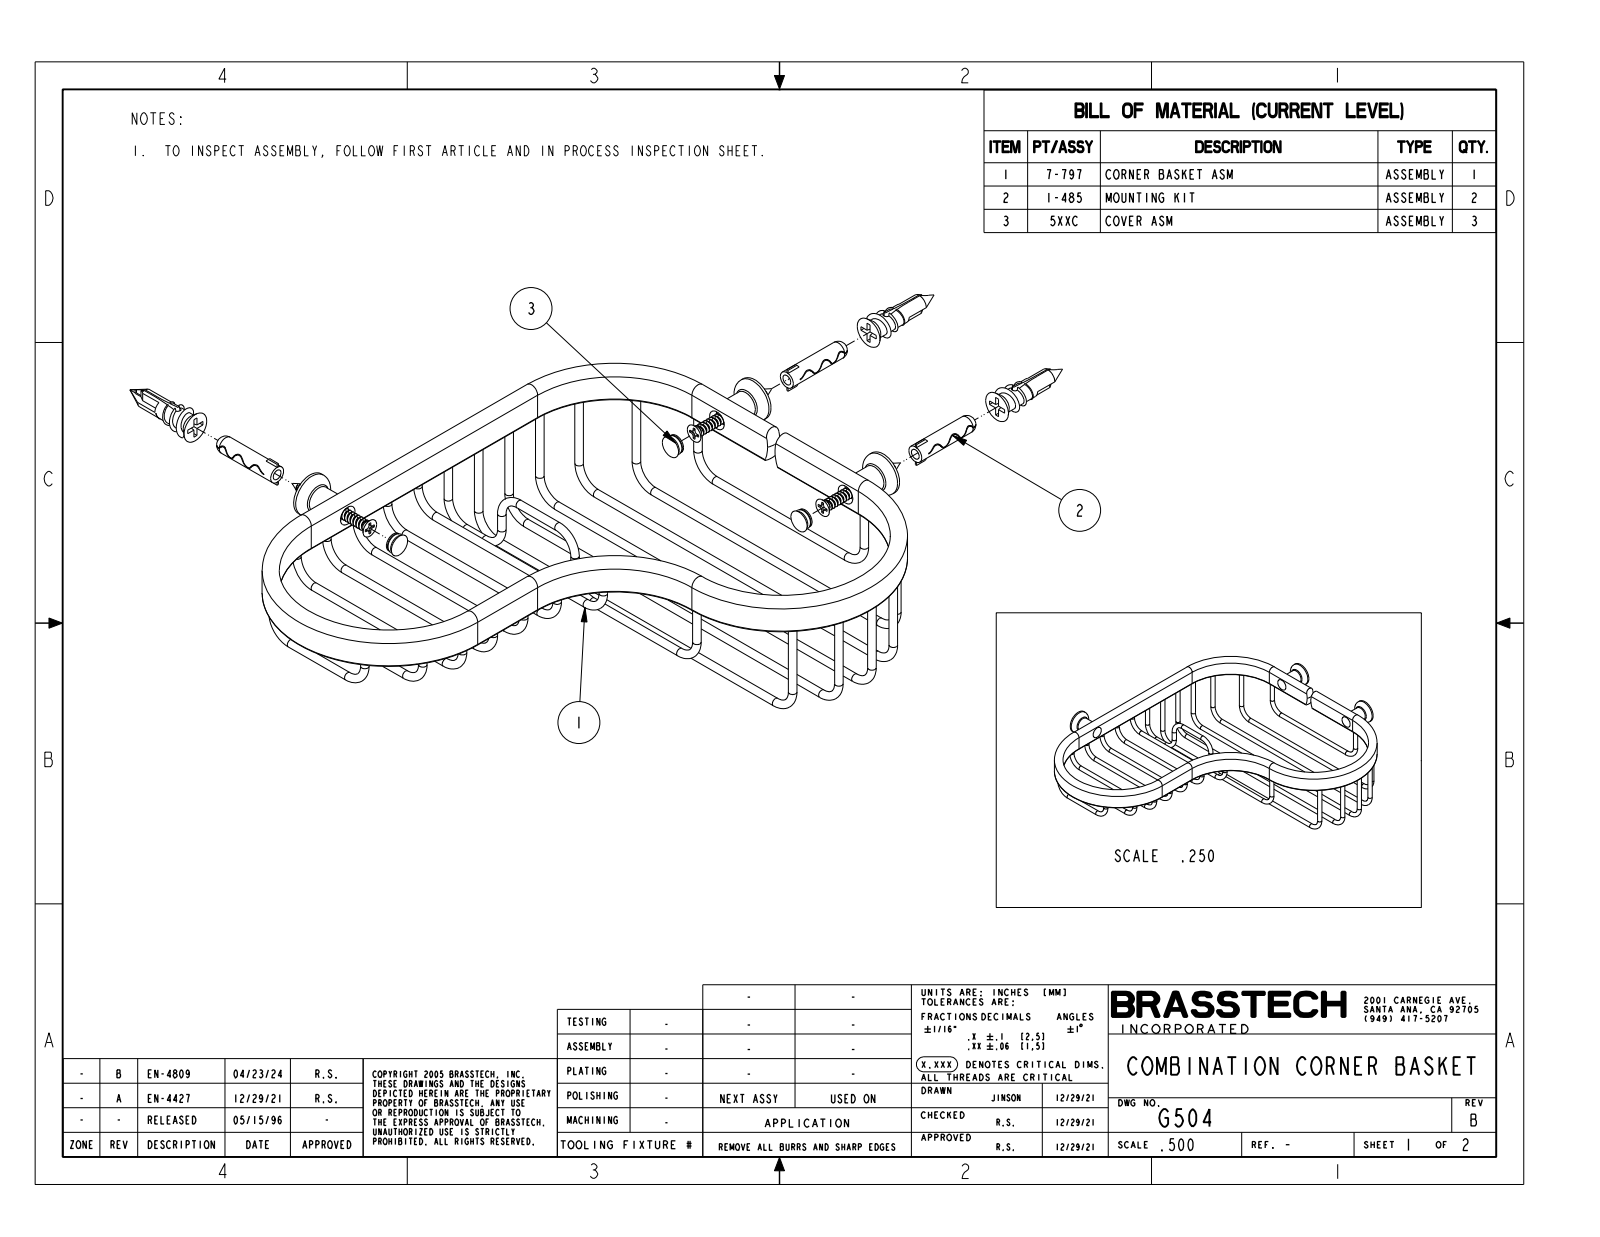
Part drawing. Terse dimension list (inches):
name: G504
written by: CREO PARAMETRIC BY PTC INC, 2018400 (CONFIG_CONTROL_DESIGN)
unit: in
bodies: 1 solid, 234 faces (12 planar, 124 cylindrical, 98 other)
size: 8.374 × 7.208 × 2.019
volume: 3.869 in³; area: 65.65 in²
bosses: 45× ⌀0.118, 3× ⌀0.63, 3× ⌀0.375
rounds: 6× R0.02, 4× R1.5, 4× R1.736, 3× R0.118
face distances: 0.236, 0.236, 0.5, 0.736, 3.236, 3, 3.472, 3.236, 0.736, 3.736
